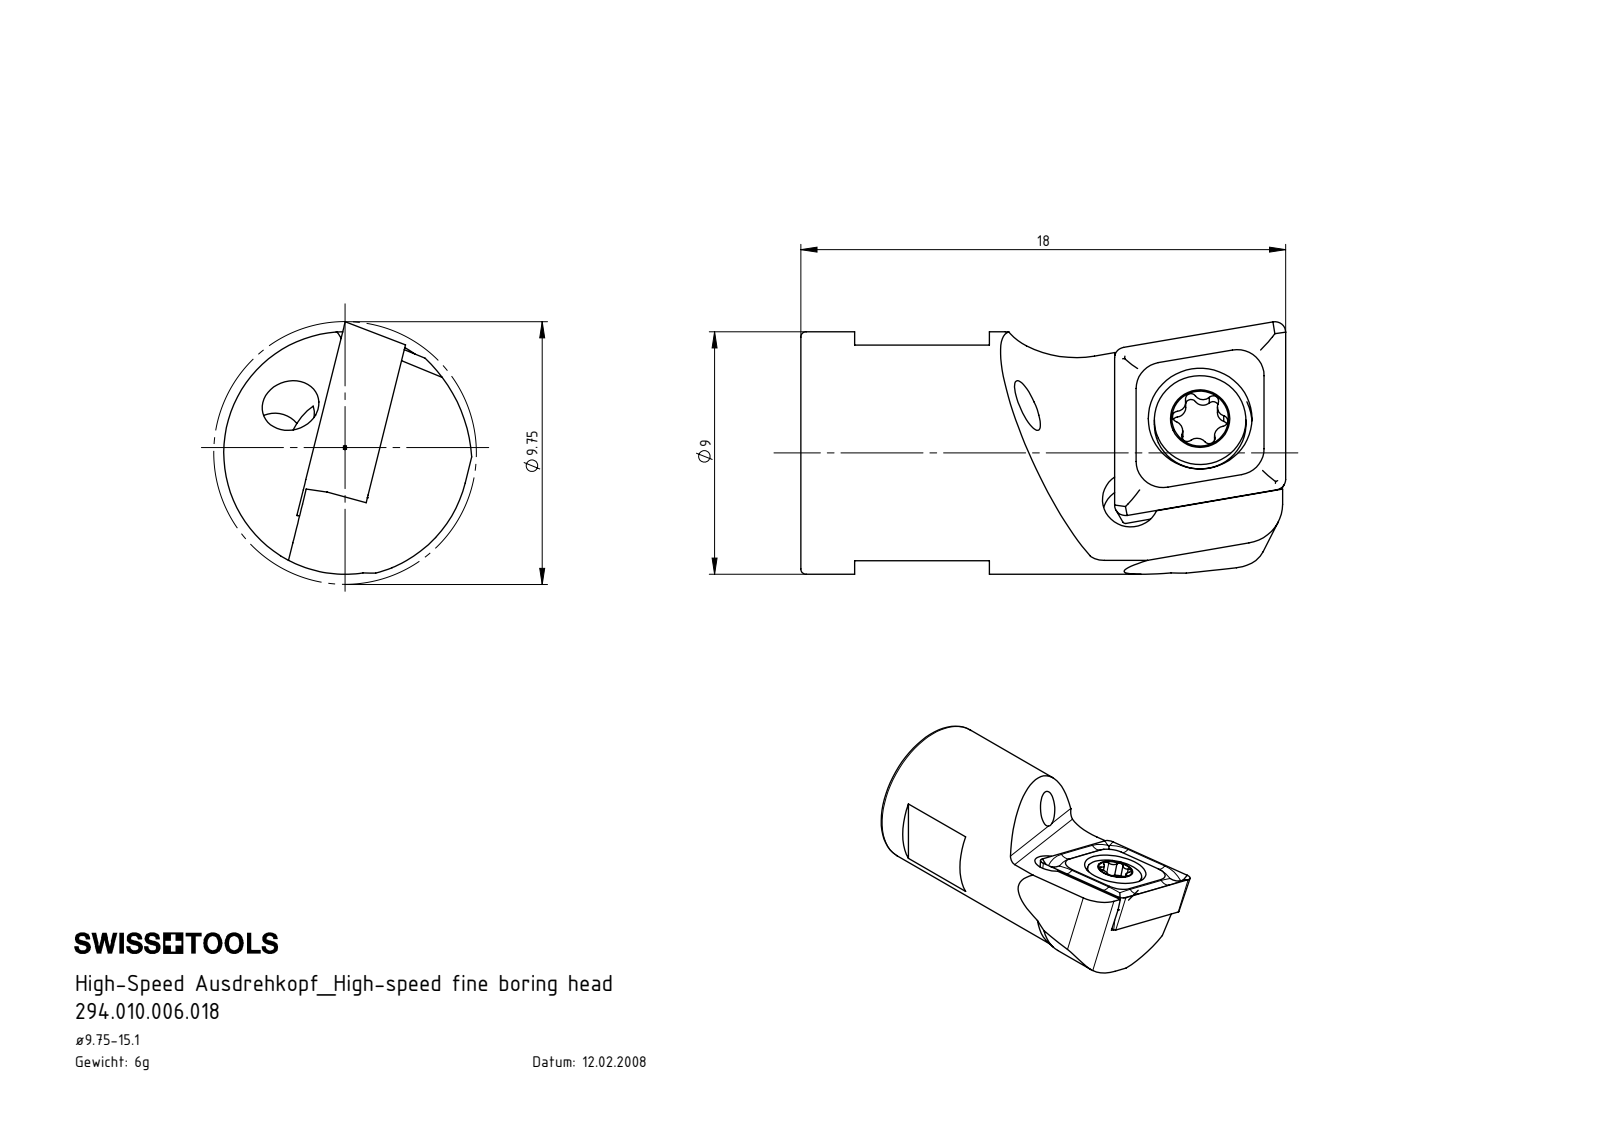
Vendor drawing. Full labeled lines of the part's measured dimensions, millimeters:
Part name (STEP PRODUCT): CCMT060204; HS5-A10.K11.018_D; HS5.A10.K11.018; WCA-ER2.001.005_B
STEP written by: SolidWorks 2017 (AUTOMOTIVE_DESIGN)
Units: millimetres
Bodies: 3 solids, 130 faces (40 planar, 39 cylindrical, 51 other)
Overall size (bounding box): 18 × 9.37 × 9.21
Volume: 751 mm³ · Surface area: 905 mm²
Round holes (diameter × count): ⌀2 ×1, ⌀2.05 ×1, ⌀2.1 ×1, ⌀2.8 ×1, ⌀3.85 ×1, ⌀4.2 ×1
Round bosses / shafts (diameter × count): ⌀9 ×1, ⌀3.4 ×1, ⌀2.5 ×1
Partial cylindrical surfaces — rounded edges, fillets, slot ends (radius × count): R0.21 ×6, R0.36 ×5, R0.36 ×1, R0.5 ×1, R1.5 ×1, R4 ×1, R4.6 ×1, R5.5 ×1
Main face-to-face distances: 2.28, 8, 2.38, 11.76, 5, 2, 9.76, 7, 4.76, 1.48
Hole centre spacings: 4.01
